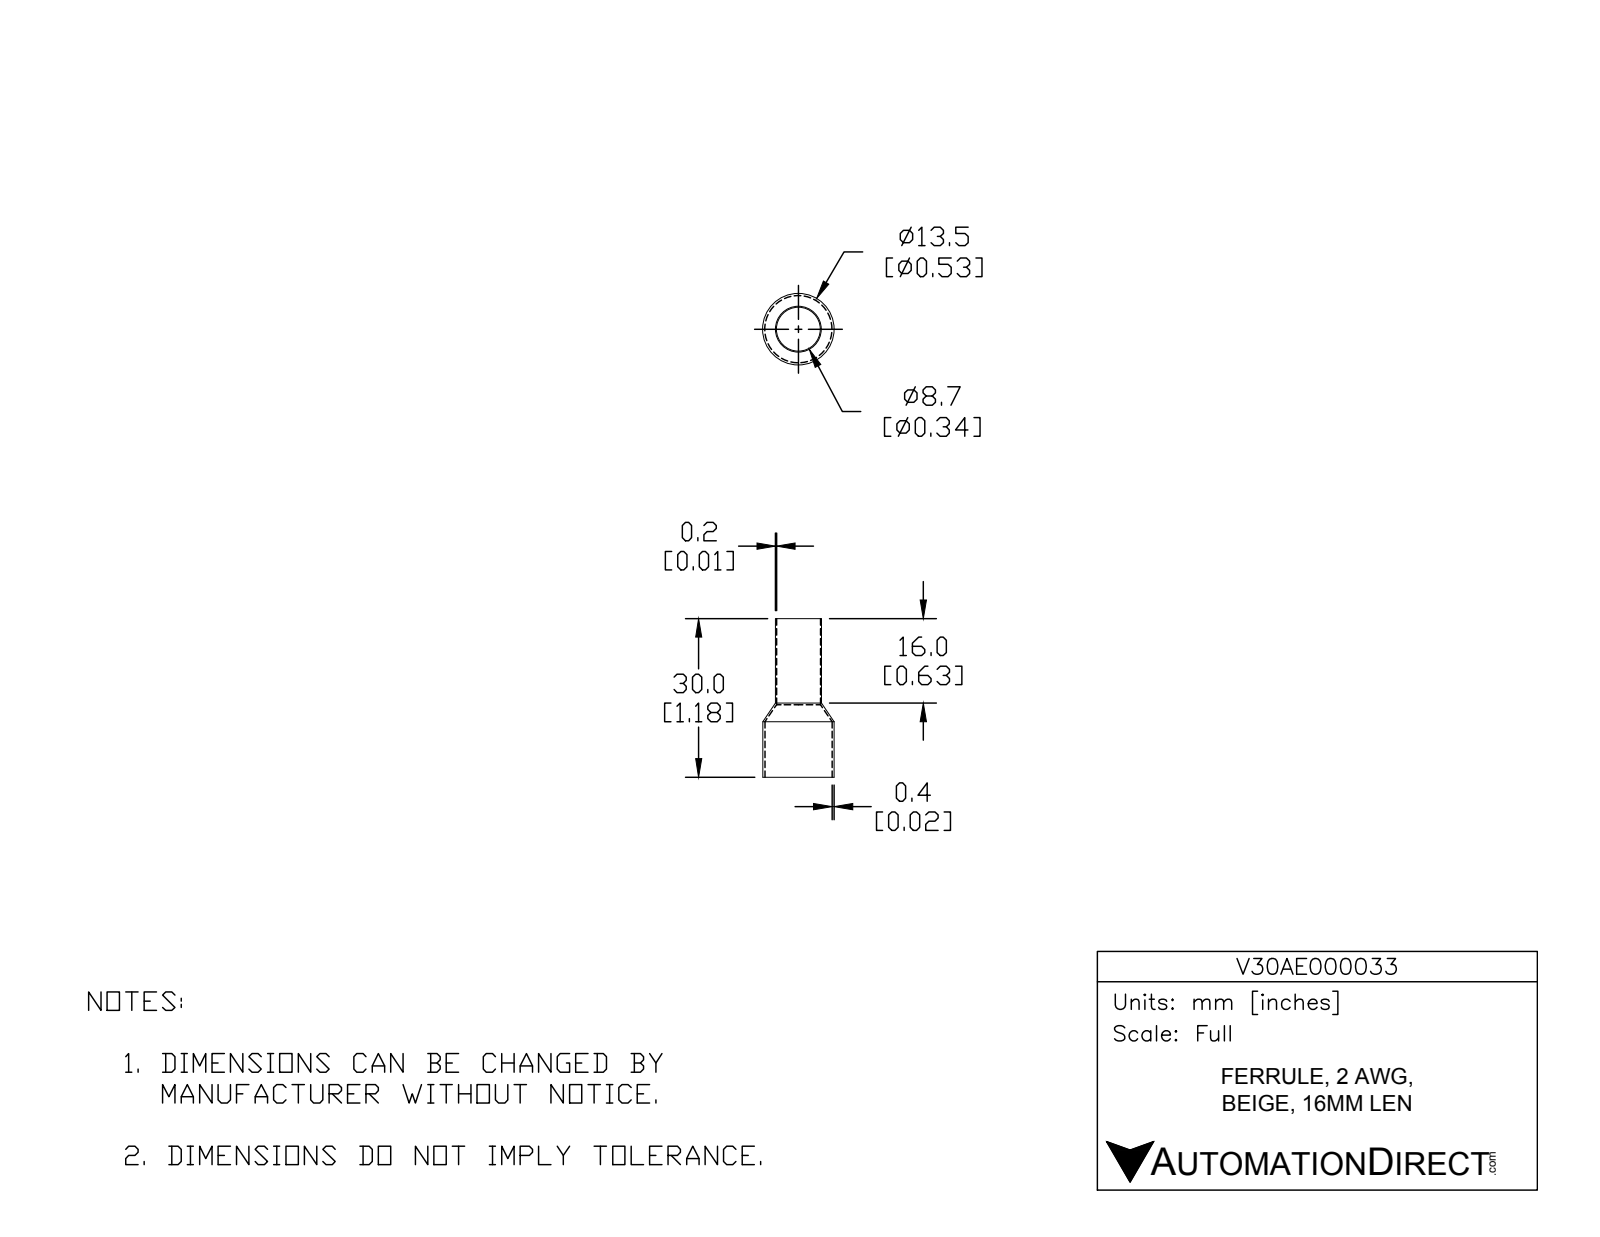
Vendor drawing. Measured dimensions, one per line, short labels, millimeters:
name: V30AE000033
written by: SolidWorks 2017 (AUTOMOTIVE_DESIGN)
unit: mm
bodies: 1 solid, 14 faces (2 planar, 8 cylindrical, 4 other)
size: 30 × 13.5 × 13.5
volume: 305 mm³; area: 2 024 mm²
holes: 1× ⌀8.3, 1× ⌀12.7
bosses: 1× ⌀13.5, 1× ⌀8.7
face distances: 30
